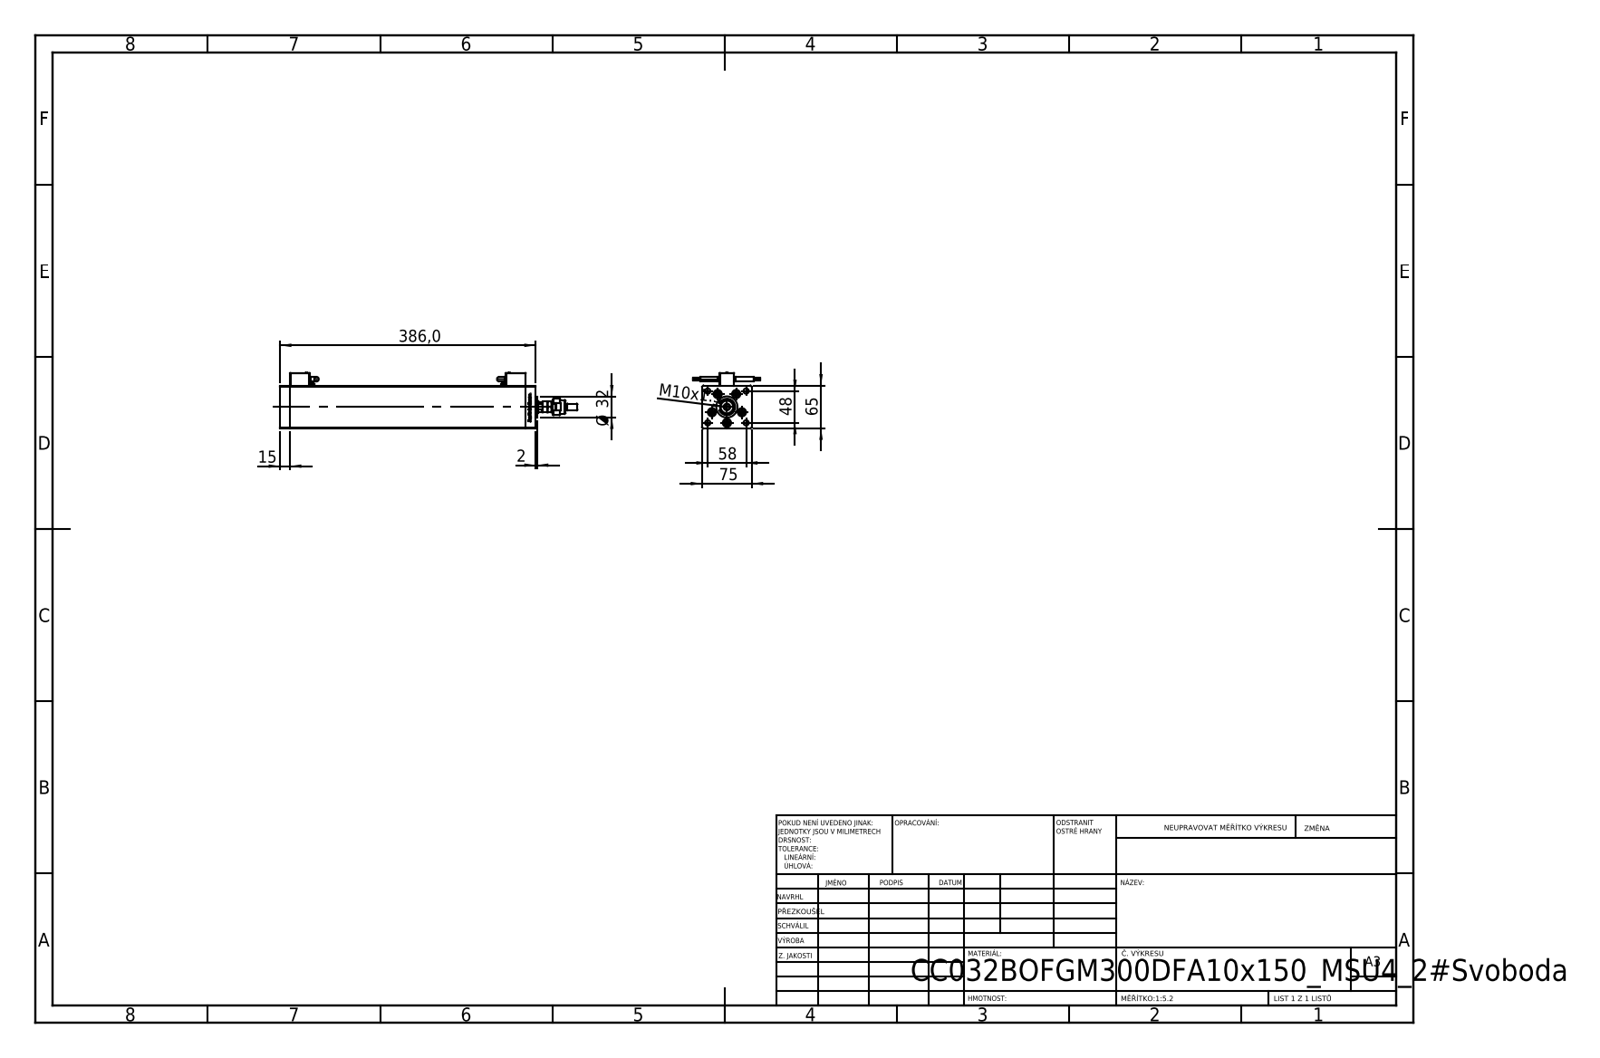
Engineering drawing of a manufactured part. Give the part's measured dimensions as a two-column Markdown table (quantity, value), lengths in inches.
| quantity | value |
| --- | --- |
| part name | V220C_B MIDDLE; V220C BACK_B; ALLEN BOLT; FEMALE_PART_FOR_DFA (+4 more) |
| STEP written by | SolidWorks 2019 (CONFIG_CONTROL_DESIGN) |
| units | inches |
| bodies | 18 solids, 1462 faces (566 planar, 242 cylindrical, 654 other) |
| overall size | 17.677 × 4 × 3.35 |
| volume | 102.7 in³ |
| surface area | 377.3 in² |
| round holes (diameter × count) | 0.354 × 5, 0.492 × 5, 0.315 × 4, 0.142 × 2, 0.197 × 2, 0.276 × 2, 0.335 × 1, 0.709 × 1 |
| round bosses / shafts (diameter × count) | 0.033 × 8, 0.315 × 6, 0.276 × 4, 0.236 × 2, 0.138 × 2, 0.098 × 2, 1.26 × 1, 0.984 × 1 |
| partial cylindrical surfaces (radius × count) | 0.039 × 24, 0.157 × 4, 0.037 × 2, 0.217 × 1, 0.335 × 1, 0.344 × 1 |
| main face-to-face distances | 2.953, 2.559, 14.016, 0.591, 14.606, 2.146, 0.413, 0.256, 2.303, 0.157 |
| hole center spacings | 0.945, 1.482, 0.325, 0.617, 0.678, 1.091, 1.135, 1.142 |
